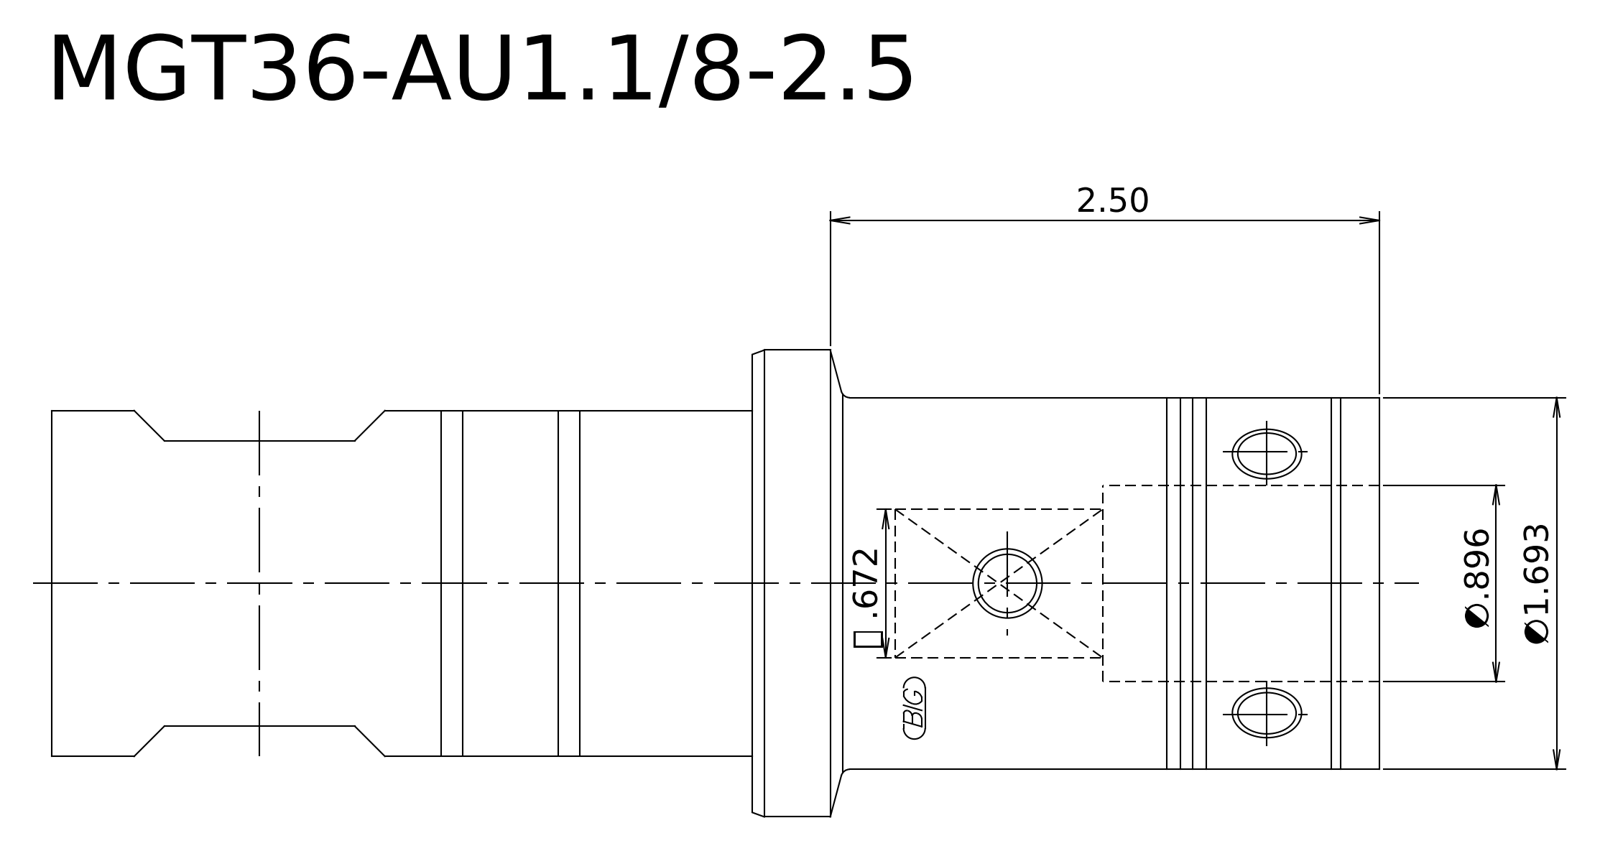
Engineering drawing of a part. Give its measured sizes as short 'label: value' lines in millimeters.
written by: Kubotek KeyCreator 2011 V10.0.2 (22737) (automotive_design)
unit: mm
bodies: 1 solid, 8 faces (3 planar, 3 cylindrical, 2 other)
size: 153.5 × 54 × 54
volume: 215 460 mm³; area: 24 557 mm²
bosses: 1× ⌀54, 1× ⌀43, 1× ⌀40
face distances: 153.5, 72.5, 81
